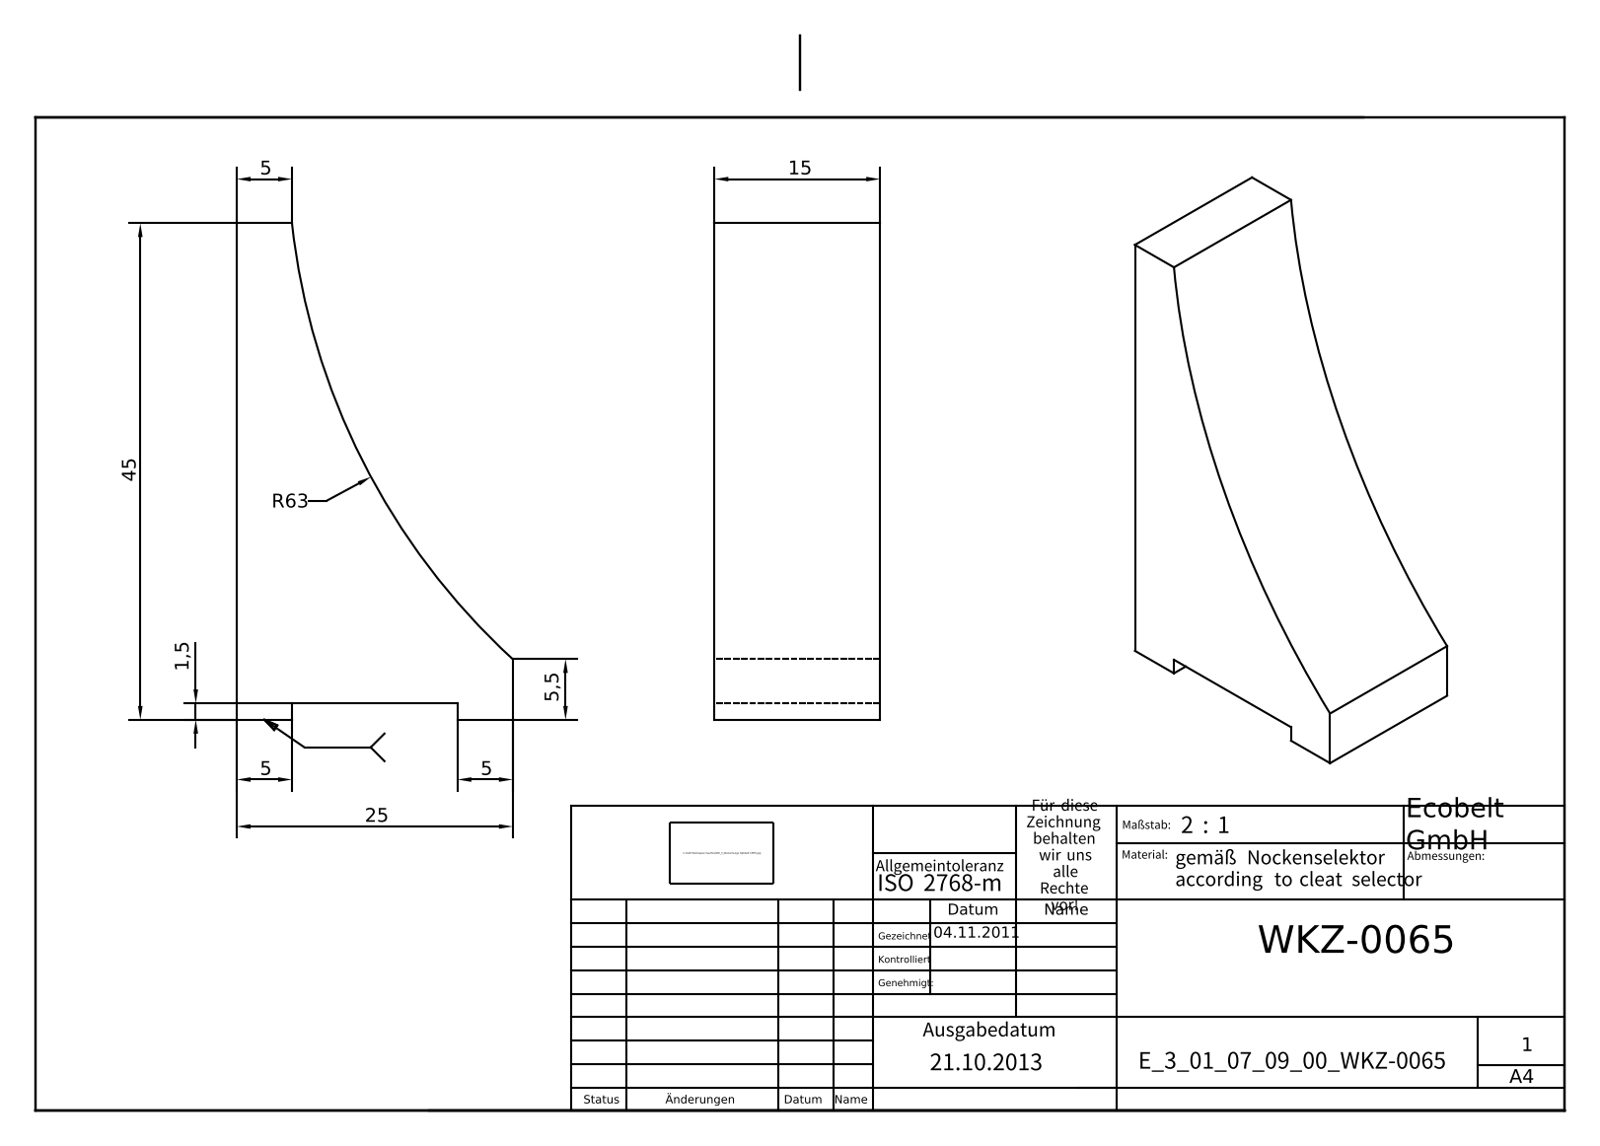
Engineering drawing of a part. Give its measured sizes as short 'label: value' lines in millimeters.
name: E_3_01_07_09_00_WKZ-0065
written by: Autodesk Inventor 2025 (AUTOMOTIVE_DESIGN)
unit: mm
bodies: 1 solid, 11 faces (10 planar, 1 cylindrical, 0 other)
size: 45 × 25 × 15
volume: 8 822 mm³; area: 3 107 mm²
rounds: 1× R63
face distances: 15, 1.5, 25, 45, 43.5, 5, 20
